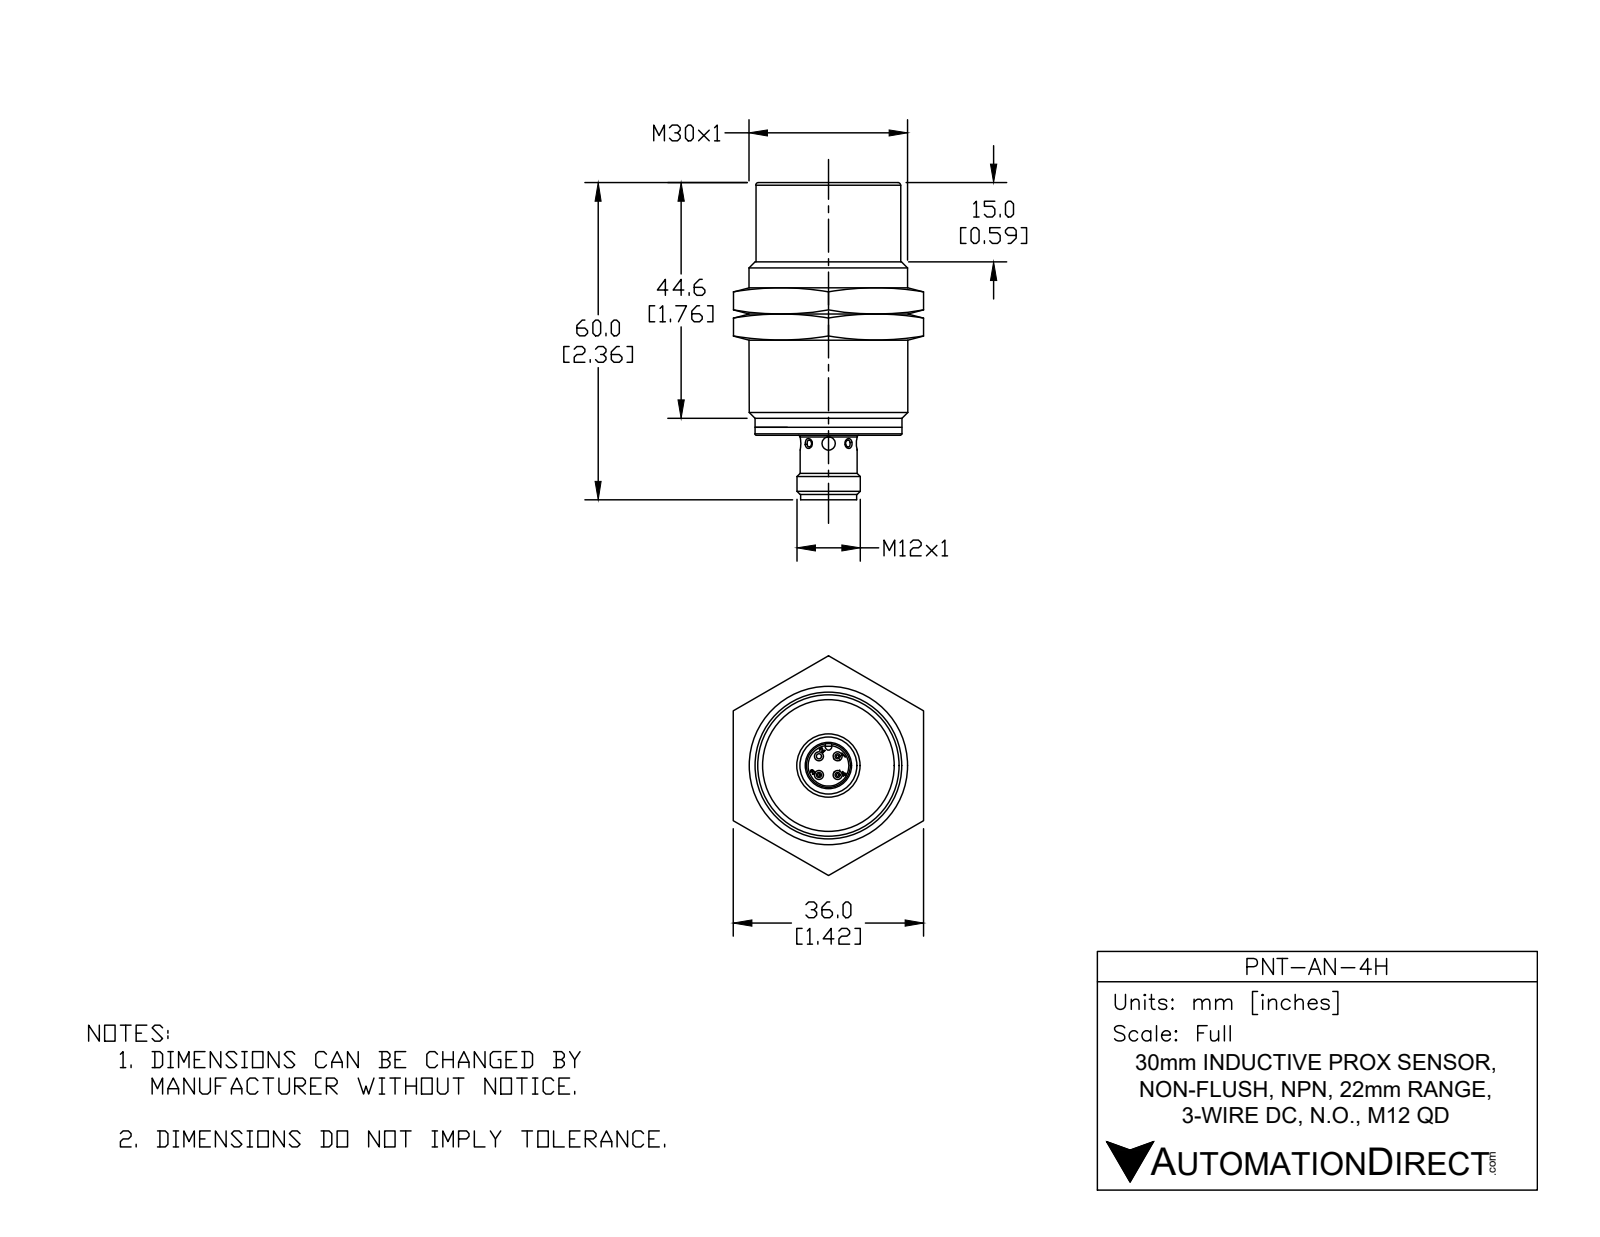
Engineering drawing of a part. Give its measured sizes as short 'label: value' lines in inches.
name: PNT-AN-4H
written by: SolidWorks 2017 (AUTOMOTIVE_DESIGN)
unit: in
bodies: 1 solid, 660 faces (260 planar, 164 cylindrical, 236 other)
size: 2.362 × 1.181 × 1.181
volume: 1.934 in³; area: 25.17 in²
holes: 3× ⌀0.043, 2× ⌀0.04, 2× ⌀0.098, 1× ⌀0.038, 1× ⌀0.04, 1× ⌀0.323, 1× ⌀0.327, 1× ⌀0.394, 1× ⌀1.047, 1× ⌀1.076
bosses: 9× ⌀0.039, 1× ⌀1.181, 1× ⌀1.094, 1× ⌀1.083, 1× ⌀1.074, 1× ⌀1.044, 1× ⌀1.037, 1× ⌀1.021
rounds: 12× R0.004, 8× R0.02, 6× R0.157, 3× R0.03, 3× R0.039, 1× R0.024, 1× R0.031
face distances: 0.157, 1.882, 1.724, 0.037, 0.12, 1.844, 1.854, 0.13, 0.031, 0.028
hole spacings: 0.098, 0.139, 0.197
